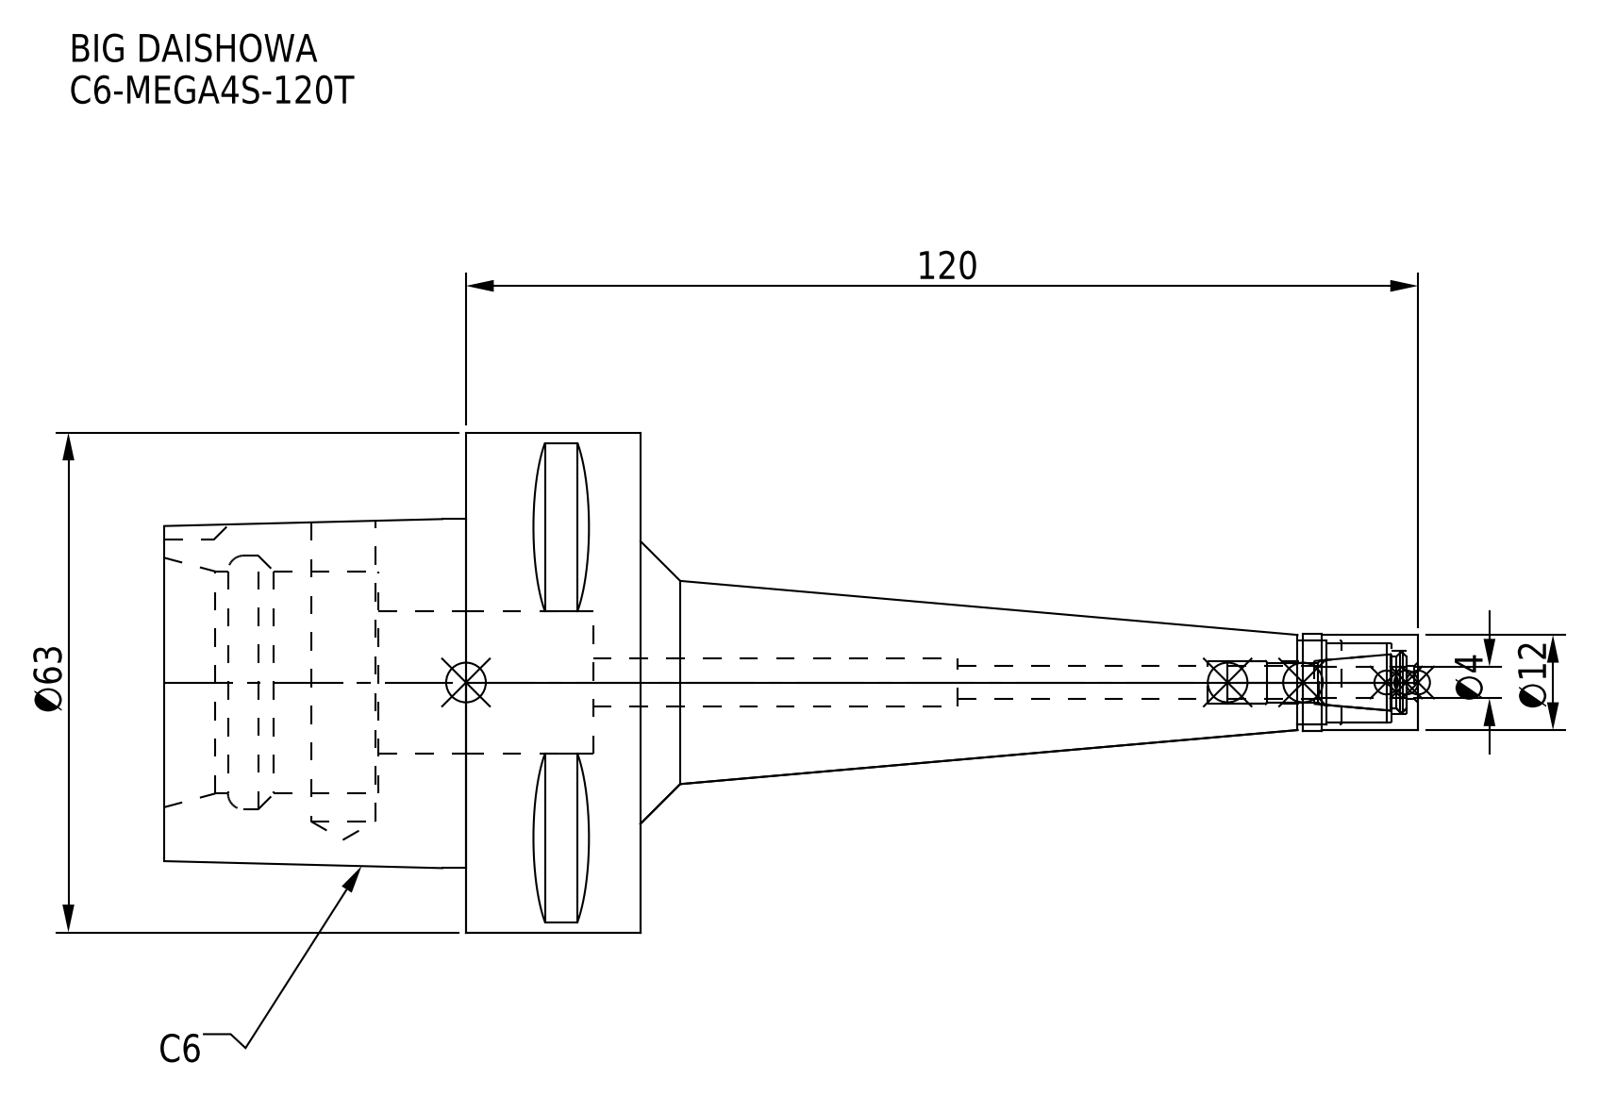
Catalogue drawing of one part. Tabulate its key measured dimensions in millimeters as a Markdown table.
| quantity | value |
| --- | --- |
| part name | C6-MEGA4S-120T-040.stp; MGN4S_1.stp; C6-MEGA4S-120T; C6-MEGA4S-120T_1.stp (+3 more) |
| STEP written by | SolidWorks 2019 (CONFIG_CONTROL_DESIGN) |
| units | millimeters |
| bodies | 2 solids, 93 faces (38 planar, 37 cylindrical, 18 other) |
| overall size | 158 × 63 × 63 |
| volume | 122 064 mm³ |
| surface area | 27 736 mm² |
| round holes (diameter × count) | 4.1 × 1, 4.2 × 1, 5.4 × 1, 6 × 1, 8 × 1, 8.1 × 1, 10 × 1, 10.5 × 1, 18 × 1, 28 × 1, 32 × 1 |
| round bosses / shafts (diameter × count) | 63 × 1, 12.3 × 1, 12 × 1 |
| partial cylindrical surfaces (radius × count) | 5 × 1 |
| main face-to-face distances | 22, 27, 60, 38, 33, 11, 24.89, 55.4, 54, 6 |
